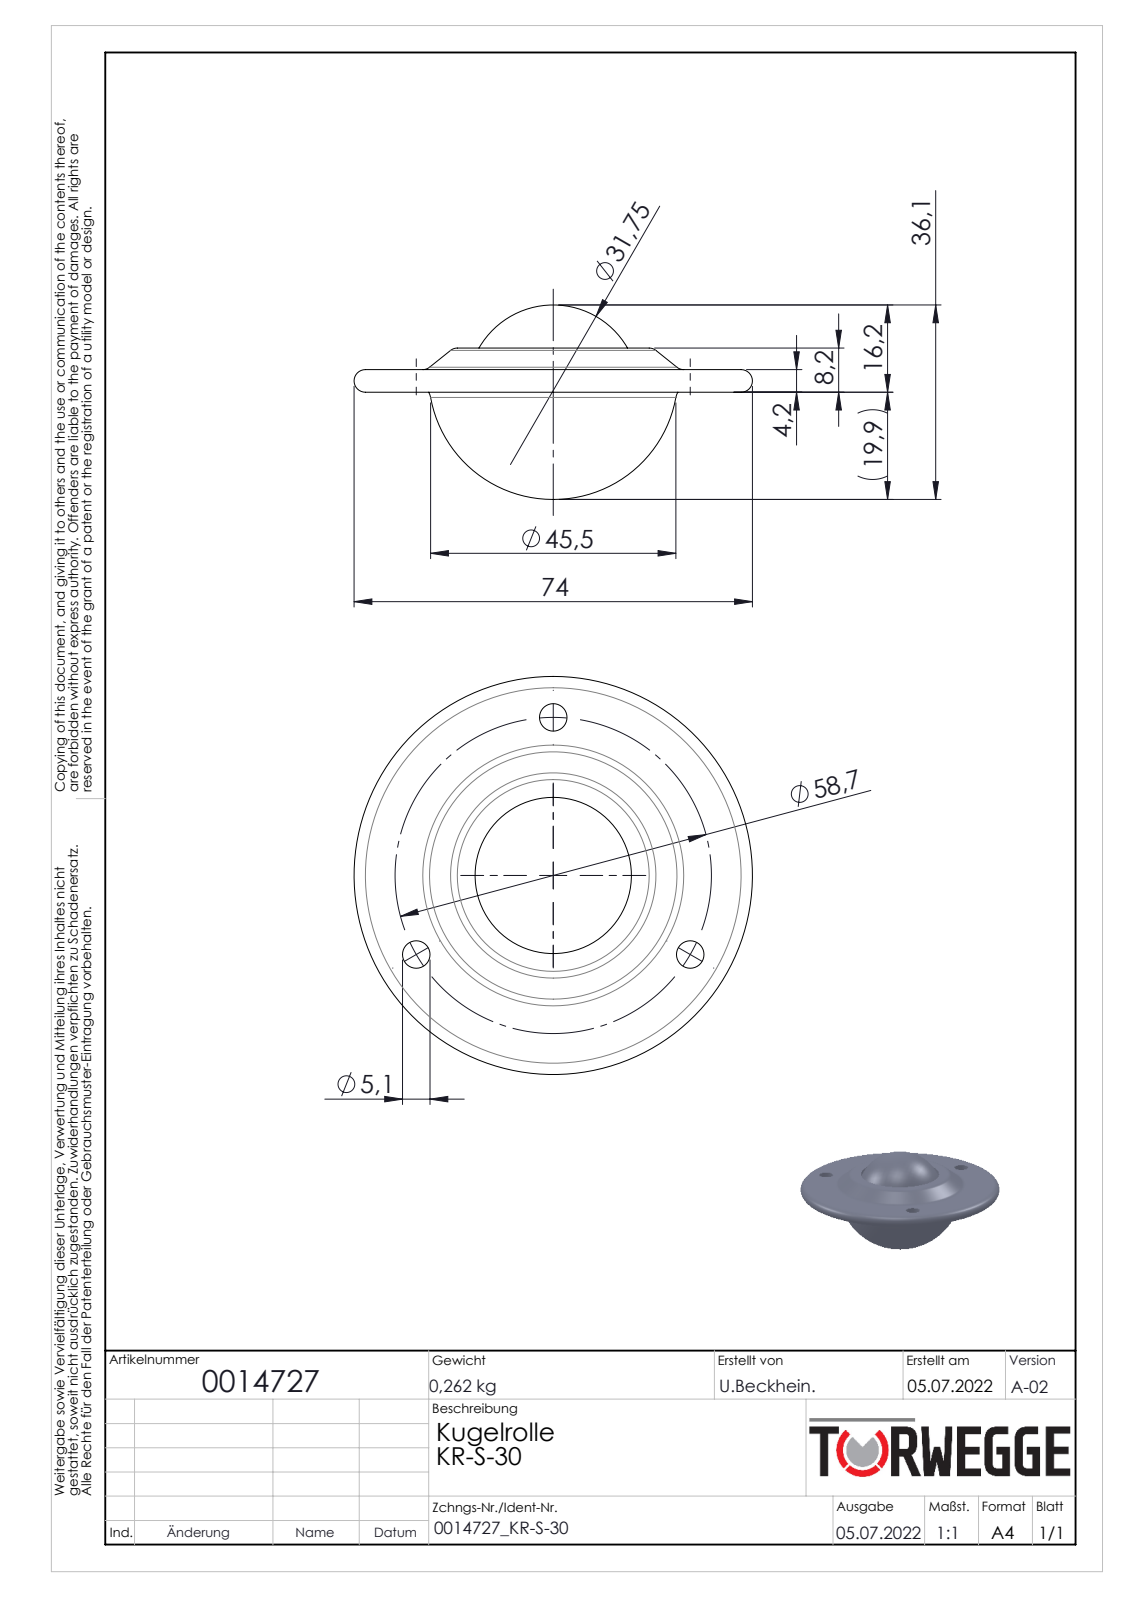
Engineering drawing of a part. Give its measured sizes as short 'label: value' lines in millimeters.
name: 0014727
written by: SolidWorks 2020 (AUTOMOTIVE_DESIGN)
unit: mm
bodies: 1 solid, 31 faces (5 planar, 12 cylindrical, 14 other)
size: 73.9 × 73.9 × 36.1
volume: 43 709 mm³; area: 12 916 mm²
holes: 3× ⌀5.1, 1× ⌀29, 1× ⌀31.75, 1× ⌀65
face distances: 2.71, 1.5, 4.21, 8.21, 6.71, 4, 7.54, 6.04, 3.33, 0.67
hole spacings: 29.34, 50.82
